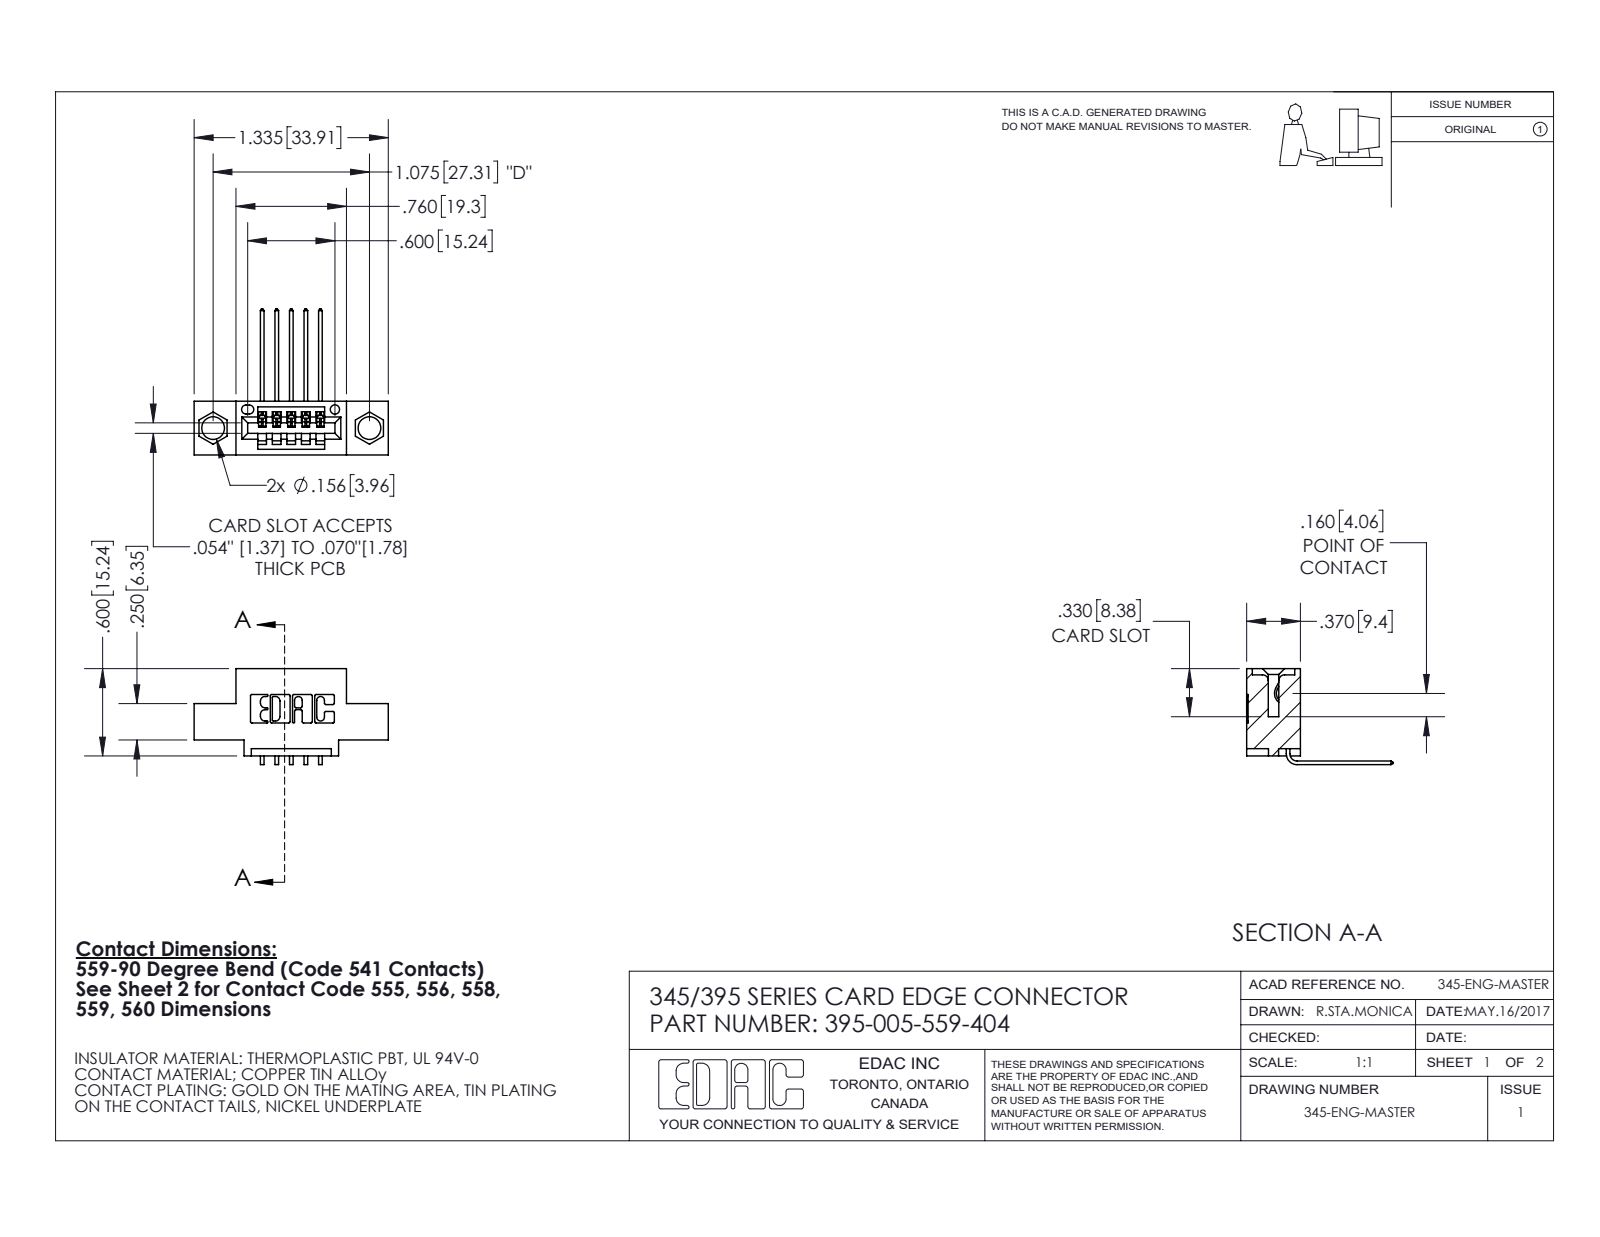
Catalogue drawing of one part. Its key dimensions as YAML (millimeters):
part_name: "395-005-559-404; 345 Part_0.110 Offset - 0.156 Dia-TI; 345-292-001_558 559 Tail - 1"
step_written_by: "SolidWorks 2020 (CONFIG_CONTROL_DESIGN)"
units: millimeters
bodies: {solids: 6, faces: 444, planar: 308, cylindrical: 136, other: 0}
overall_size: [33.9, 25.5, 16.7]
volume: 2750
surface_area: 3181
round_holes:
  - {diameter: 4, count: 2}
  - {diameter: 1.6, count: 1}
partial_cylinders:
  - {radius: 0.3, count: 22}
  - {radius: 0.2, count: 10}
  - {radius: 0.2, count: 6}
  - {radius: 0.8, count: 6}
  - {radius: 0.7, count: 3}
  - {radius: 0.8, count: 2}
  - {radius: 1, count: 2}
  - {radius: 0.4, count: 1}
face_to_face_distances: [9.4, 5.1, 2.5, 1.8, 7.6, 6.4, 0.6, 1.5, 4.1, 2.5]
hole_center_spacings: [6.9, 21.5, 27.3]
